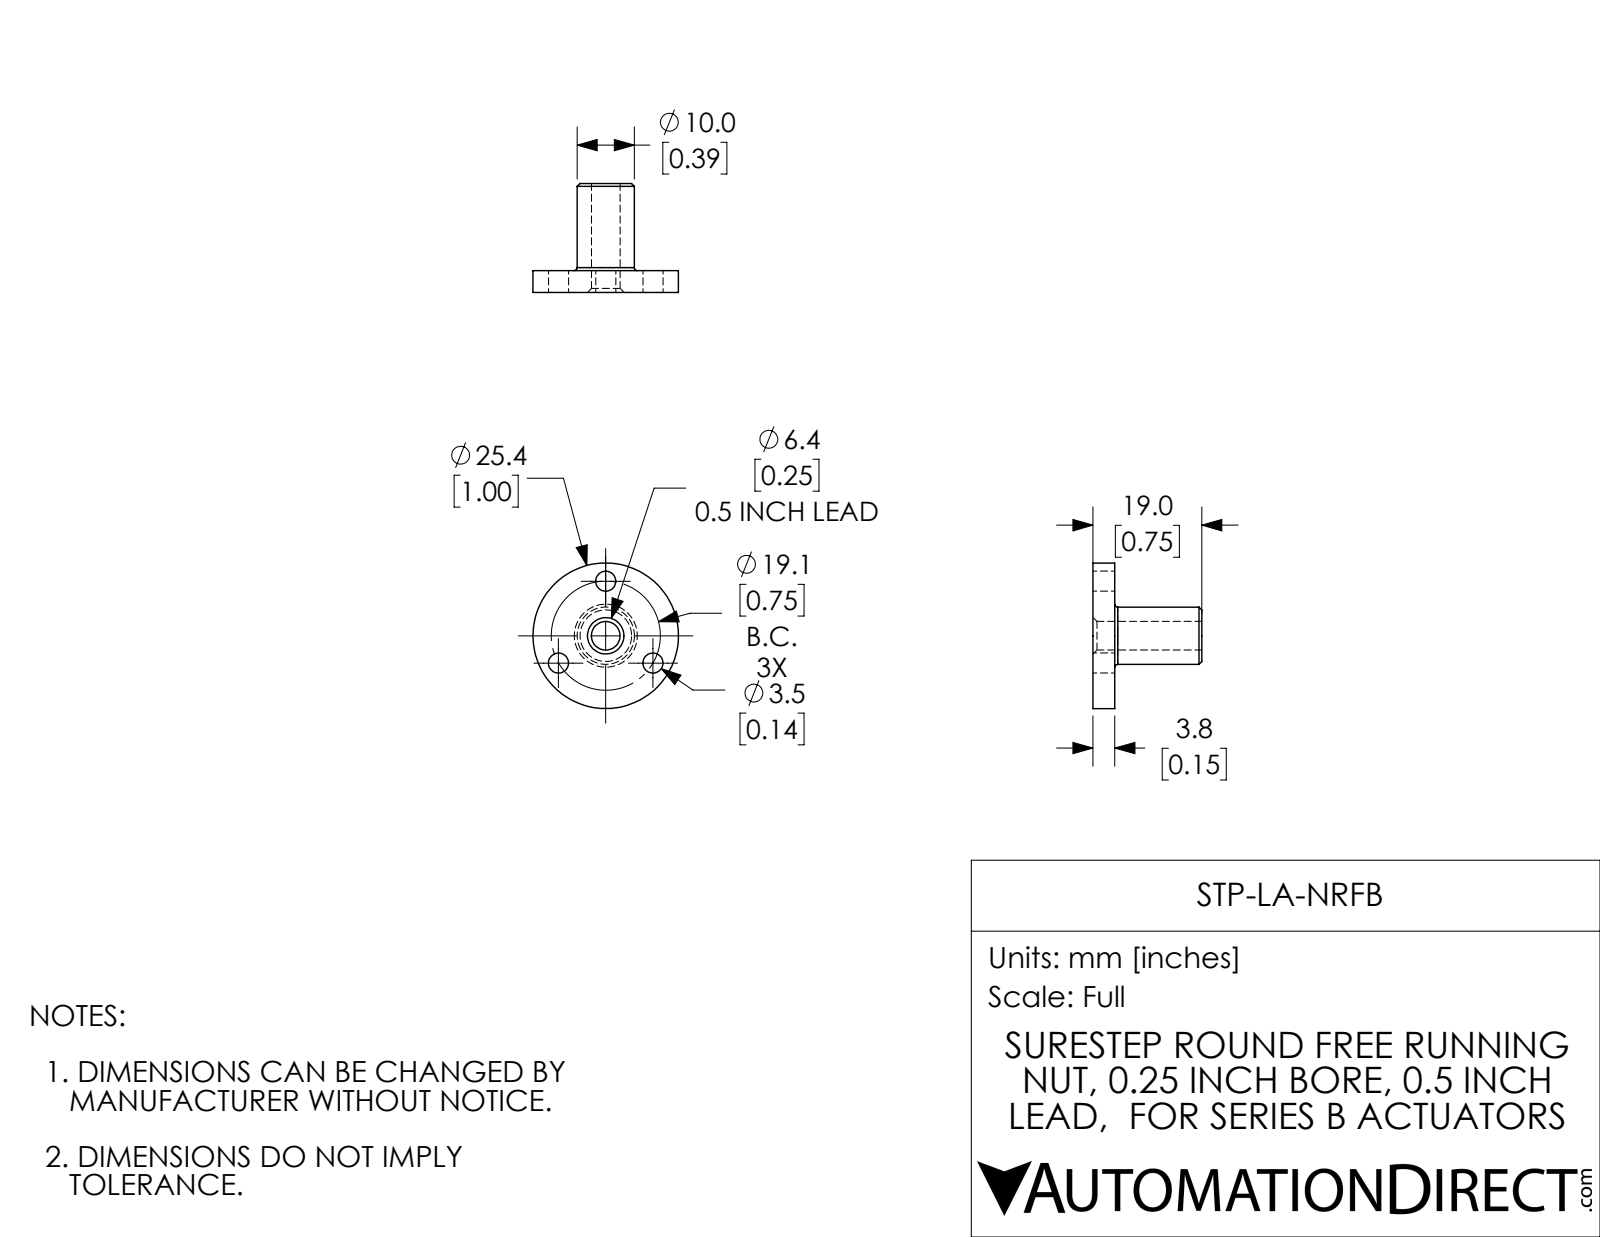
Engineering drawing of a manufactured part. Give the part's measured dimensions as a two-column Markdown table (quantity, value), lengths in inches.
| quantity | value |
| --- | --- |
| part name | STP-LA-NRFB |
| STEP written by | SolidWorks 2017 (AUTOMOTIVE_DESIGN) |
| units | inches |
| bodies | 1 solid, 21 faces (3 planar, 12 cylindrical, 6 other) |
| overall size | 1 × 1 × 0.748 |
| volume | 0.161 in³ |
| surface area | 3.255 in² |
| round holes (diameter × count) | 0.138 × 3, 0.197 × 1 |
| round bosses / shafts (diameter × count) | 1 × 1, 0.394 × 1 |
| main face-to-face distances | 0.15, 0.598, 0.748 |
| hole center spacings | 0.375, 0.649, 0.65 |
